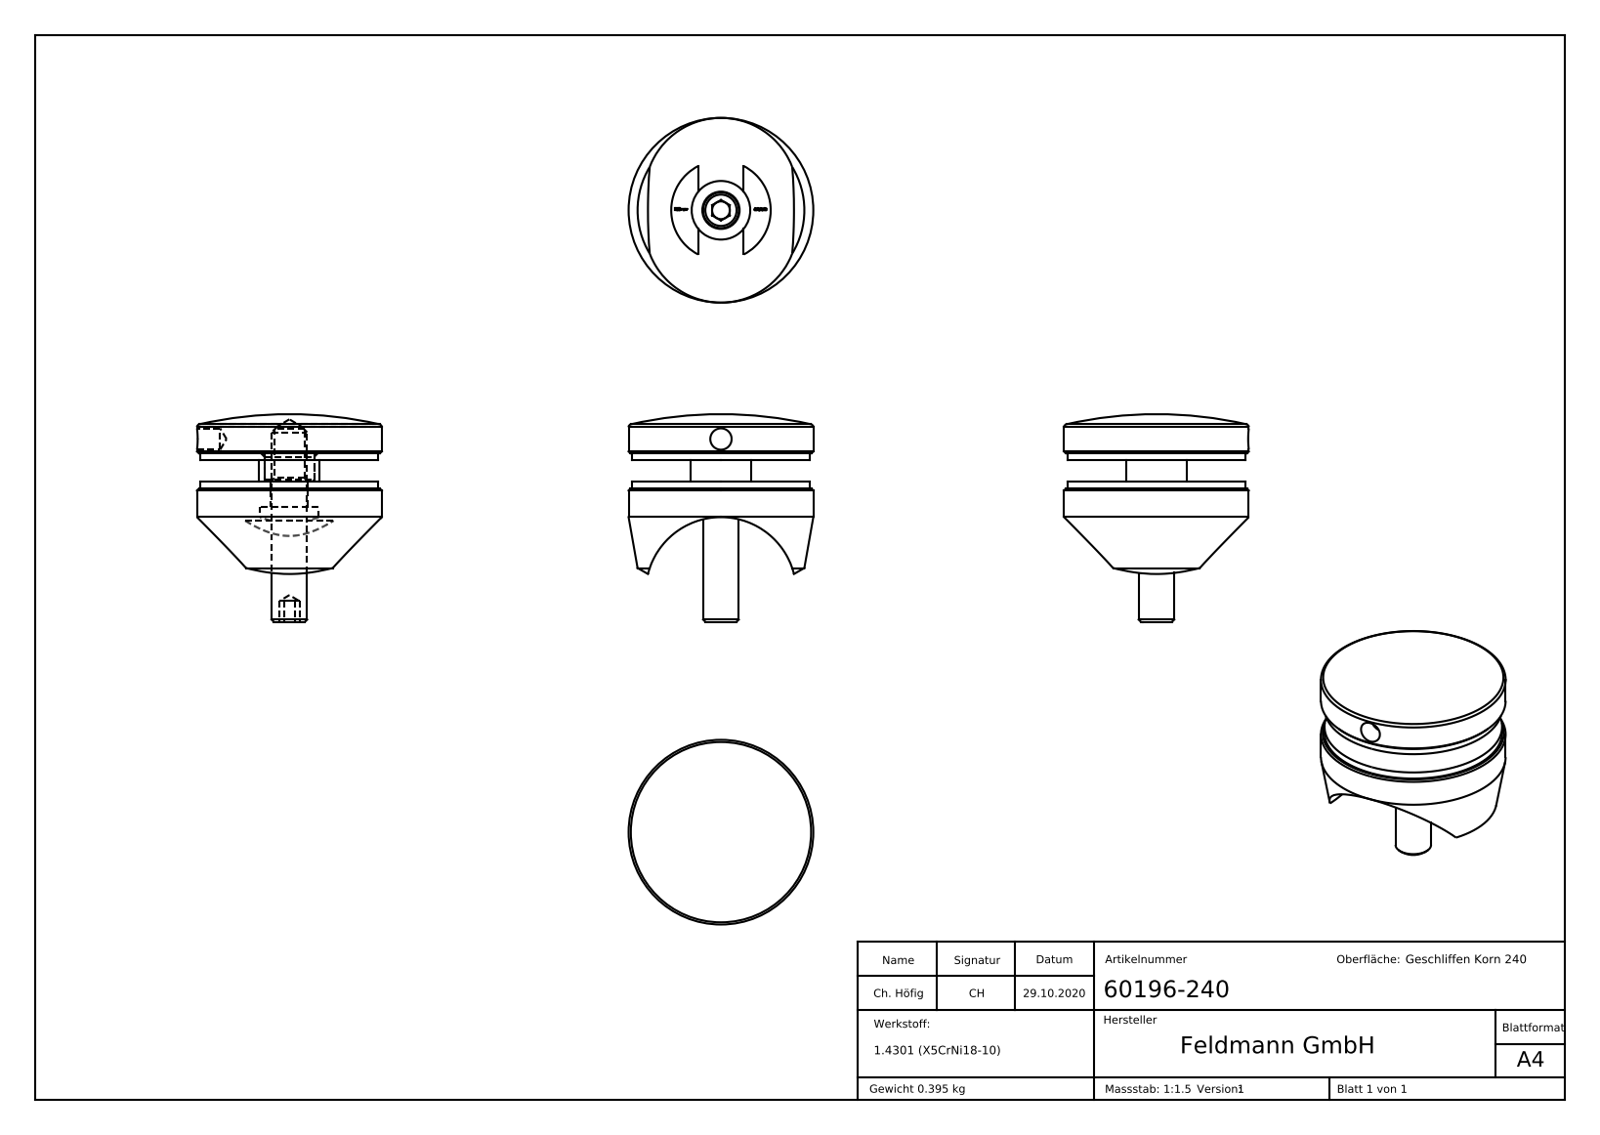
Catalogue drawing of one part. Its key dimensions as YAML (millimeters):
part_name: "6019X-240 Konfig Teil4; 6019X-240 Konfig Teil4_6019X-XXX Teil4; 6019X-240 Konfig Teil2; 6019X-240 Konfig Teil1_6019X-240 Teil1 (+7 more)"
step_written_by: "SolidWorks 2018 (CONFIG_CONTROL_DESIGN)"
units: millimeters
bodies: {solids: 5, faces: 302, planar: 143, cylindrical: 29, other: 130}
overall_size: [110, 52, 52]
volume: 56405
surface_area: 24397
round_holes:
  - {diameter: 6, count: 1}
  - {diameter: 8.5, count: 1}
  - {diameter: 10.5, count: 1}
  - {diameter: 14, count: 1}
  - {diameter: 16.5, count: 1}
round_bosses_or_shafts:
  - {diameter: 52, count: 1}
  - {diameter: 50, count: 1}
  - {diameter: 17, count: 1}
  - {diameter: 10, count: 1}
partial_cylinders:
  - {radius: 14, count: 1}
  - {radius: 21.2, count: 1}
face_to_face_distances: [2, 8, 10, 6, 9, 11, 17, 19, 5, 4]
